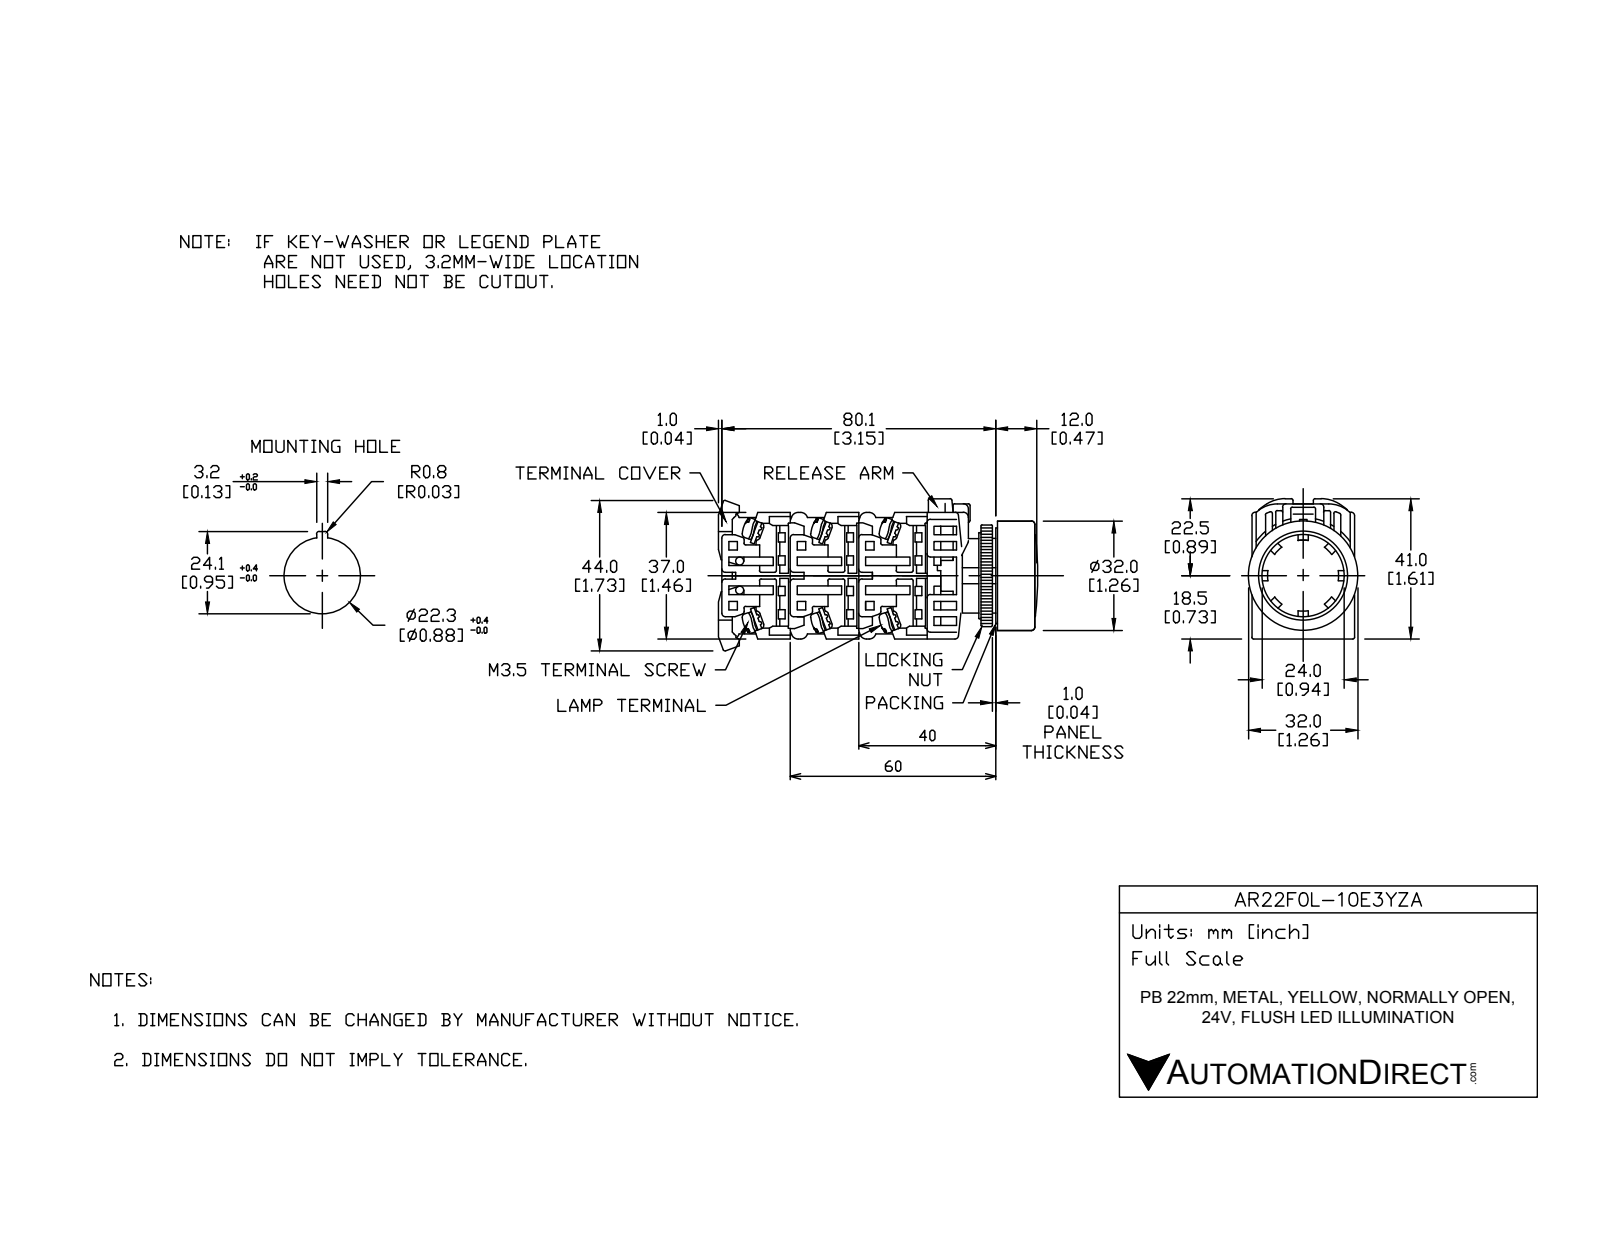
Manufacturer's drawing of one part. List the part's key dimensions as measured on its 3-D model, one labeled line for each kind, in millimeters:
Part name (STEP PRODUCT): AR22F0L-10E3YZA
STEP written by: SolidWorks 2017 (AUTOMOTIVE_DESIGN)
Units: millimetres
Bodies: 18 solids, 475 faces (329 planar, 111 cylindrical, 35 other)
Overall size (bounding box): 52.75 × 43.81 × 32
Volume: 36 367 mm³ · Surface area: 24 064 mm²
Round holes (diameter × count): ⌀21.8 ×1, ⌀22 ×1, ⌀25 ×1, ⌀31 ×1
Round bosses / shafts (diameter × count): ⌀5 ×4, ⌀32 ×1, ⌀30.5 ×1, ⌀29.8 ×1, ⌀24 ×1, ⌀23.8 ×1, ⌀21.75 ×1, ⌀17 ×1
Partial cylindrical surfaces — rounded edges, fillets, slot ends (radius × count): R0.5 ×39, R1.75 ×8, R5 ×4, R4 ×2, R16.59 ×1, R17.59 ×1
Main face-to-face distances: 1, 18, 28.5, 48.5, 20, 29, 3, 2, 21, 0.5
